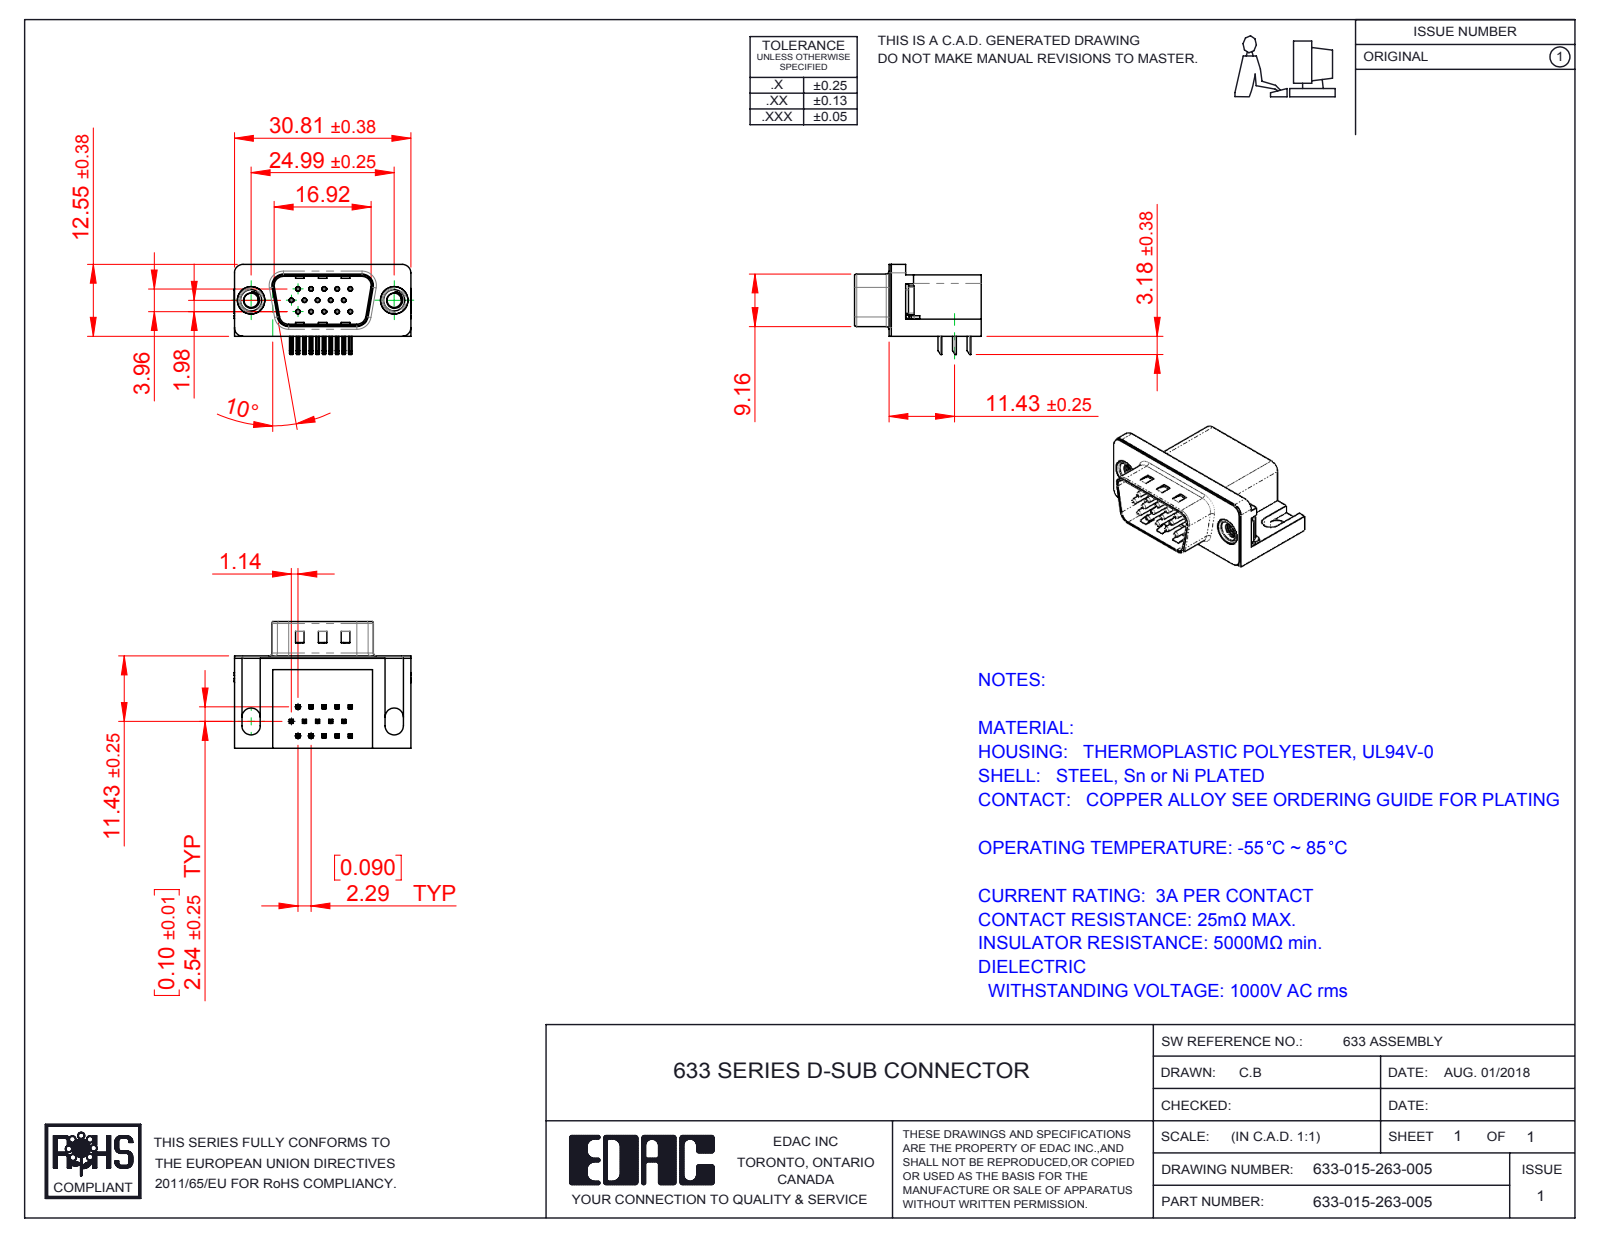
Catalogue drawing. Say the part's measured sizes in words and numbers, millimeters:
The part is named "633-015-263-005; 633 Housing_15 Contact; 633 Shell_15 Contact; 633 Contact Bottom (+4 more)". Its 3-D file was written by "SolidWorks 2016 (CONFIG_CONTROL_DESIGN)". It is 21 solids with 1439 faces: 861 planar, 443 cylindrical and 135 other. Overall it measures 30.89 by 22.1 by 15.73 millimeters. Its volume is 4 020 cubic millimeters and its surface area 5 205 square millimeters. Round holes: 15 of diameter 0.35, 15 of diameter 0.8, 2 of diameter 2.5, 2 of diameter 4, 2 of diameter 4.8, 2 of diameter 5. Round bosses or shafts: 15 of diameter 0.75, 2 of diameter 4.9, 2 of diameter 4.75, 2 of diameter 3.9. Partial cylindrical surfaces (rounded edges, fillets, slot ends): 68 of radius 0.25, 30 of radius 0.12, 16 of radius 1, 9 of radius 0.5, 8 of radius 1.6, 7 of radius 1.5, 4 of radius 0.9, 4 of radius 2. The main face-to-face distances are 0.4, 10.35, 15.7, 2.9, 16.1, 2.5, 6.7, 0.35, 10.7, 13.2. The hole center spacings are 3.96, 2.28, 4.57, 2.29, 6.05, 6.86, 7.92, 6.04.
